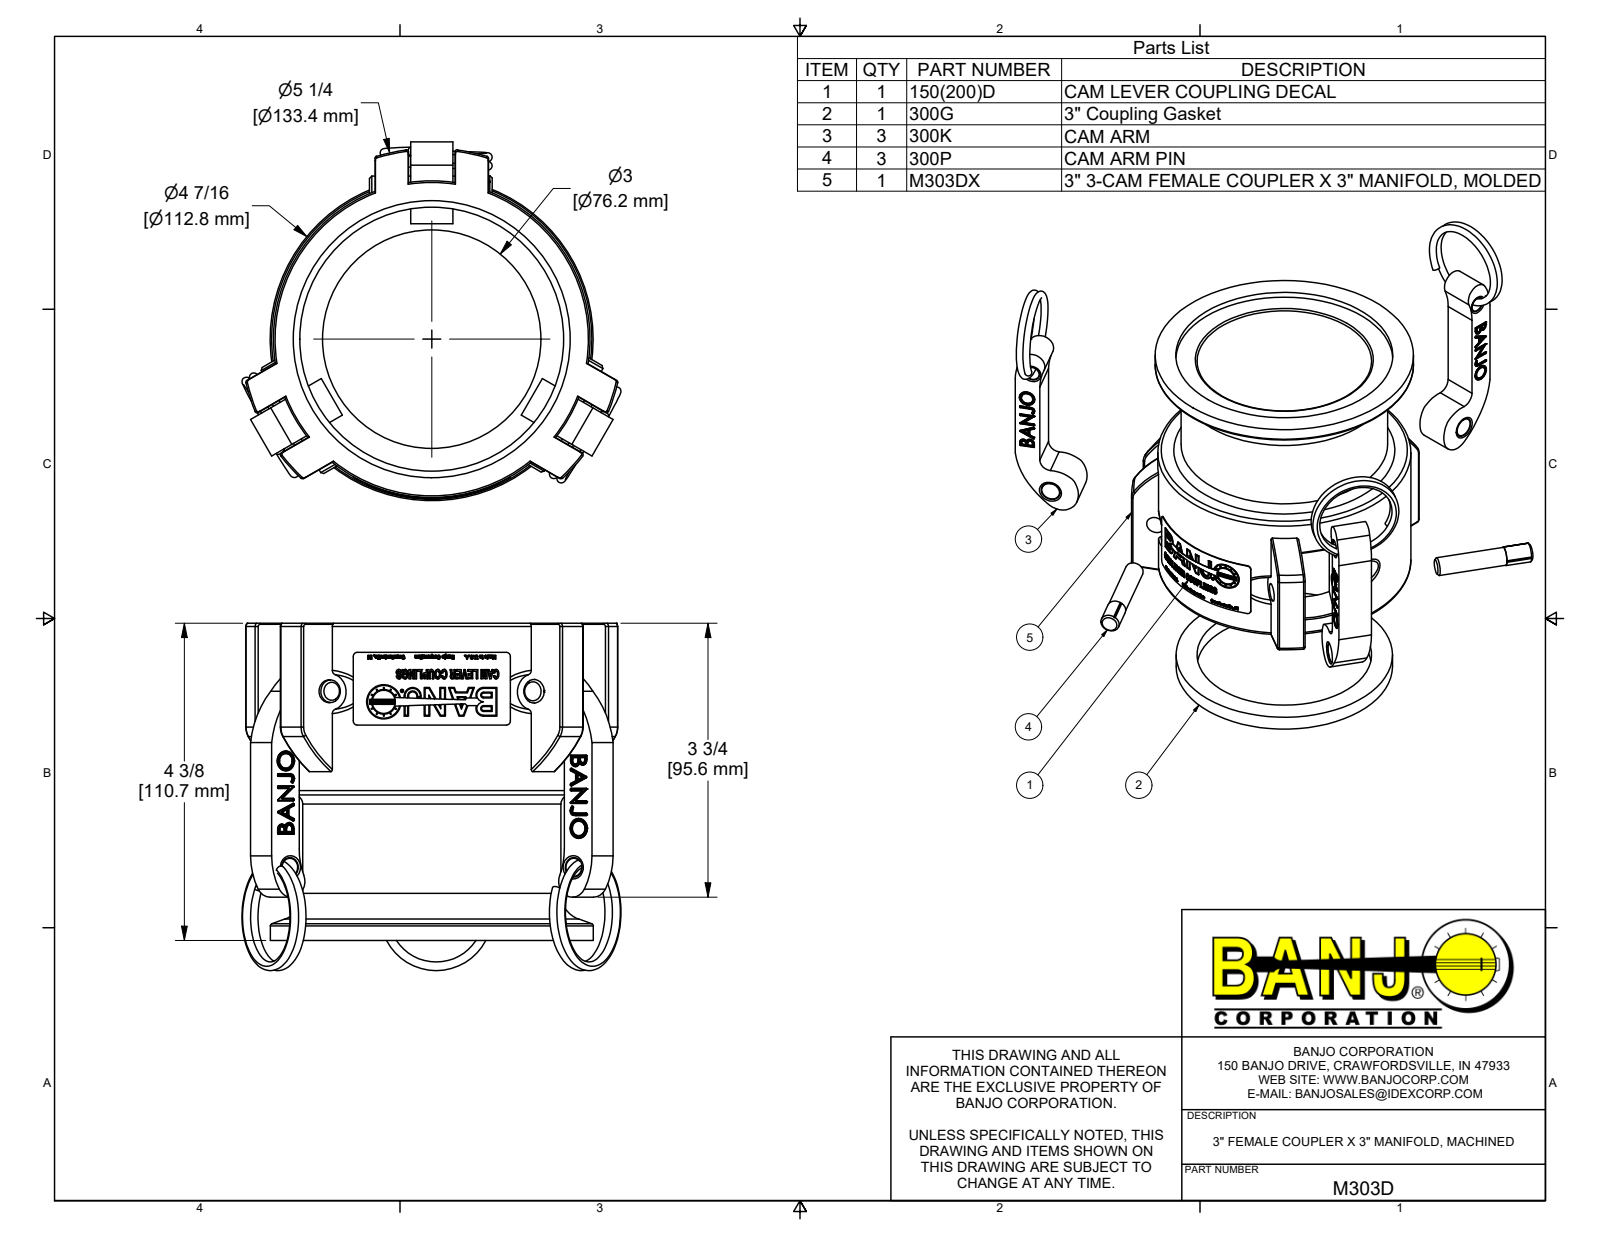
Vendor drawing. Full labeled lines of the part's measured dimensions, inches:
Part name (STEP PRODUCT): M303D; M303DX; 300G; 300P (+4 more)
STEP written by: Autodesk Inventor 2019 (AUTOMOTIVE_DESIGN)
Units: inches
Bodies: 12 solids, 3084 faces (903 planar, 788 cylindrical, 1393 other)
Overall size (bounding box): 5.211 × 4.93 × 4.789
Volume: 23.85 in³ · Surface area: 195.7 in²
Round holes (diameter × count): ⌀0.25 ×3, ⌀0.313 ×3, ⌀0.319 ×3, ⌀0.318 ×1, ⌀0.449 ×1, ⌀3 ×1, ⌀3.63 ×1, ⌀3.73 ×1, ⌀3.8 ×1
Round bosses / shafts (diameter × count): ⌀0.325 ×3, ⌀0.311 ×3, ⌀4.44 ×1, ⌀4.35 ×1, ⌀3.719 ×1, ⌀3.55 ×1, ⌀0.473 ×1
Partial cylindrical surfaces — rounded edges, fillets, slot ends (radius × count): R0.006 ×355, R0.005 ×51, R0.03 ×24, R0.929 ×6, R0.06 ×4, R0.188 ×3, R0.218 ×3, R0.25 ×3
Main face-to-face distances: 0.03, 0.61, 0.46, 0.49, 1.07, 1.1, 4.36, 0.58, 0.25, 1.805
Hole centre spacings: 2.442
